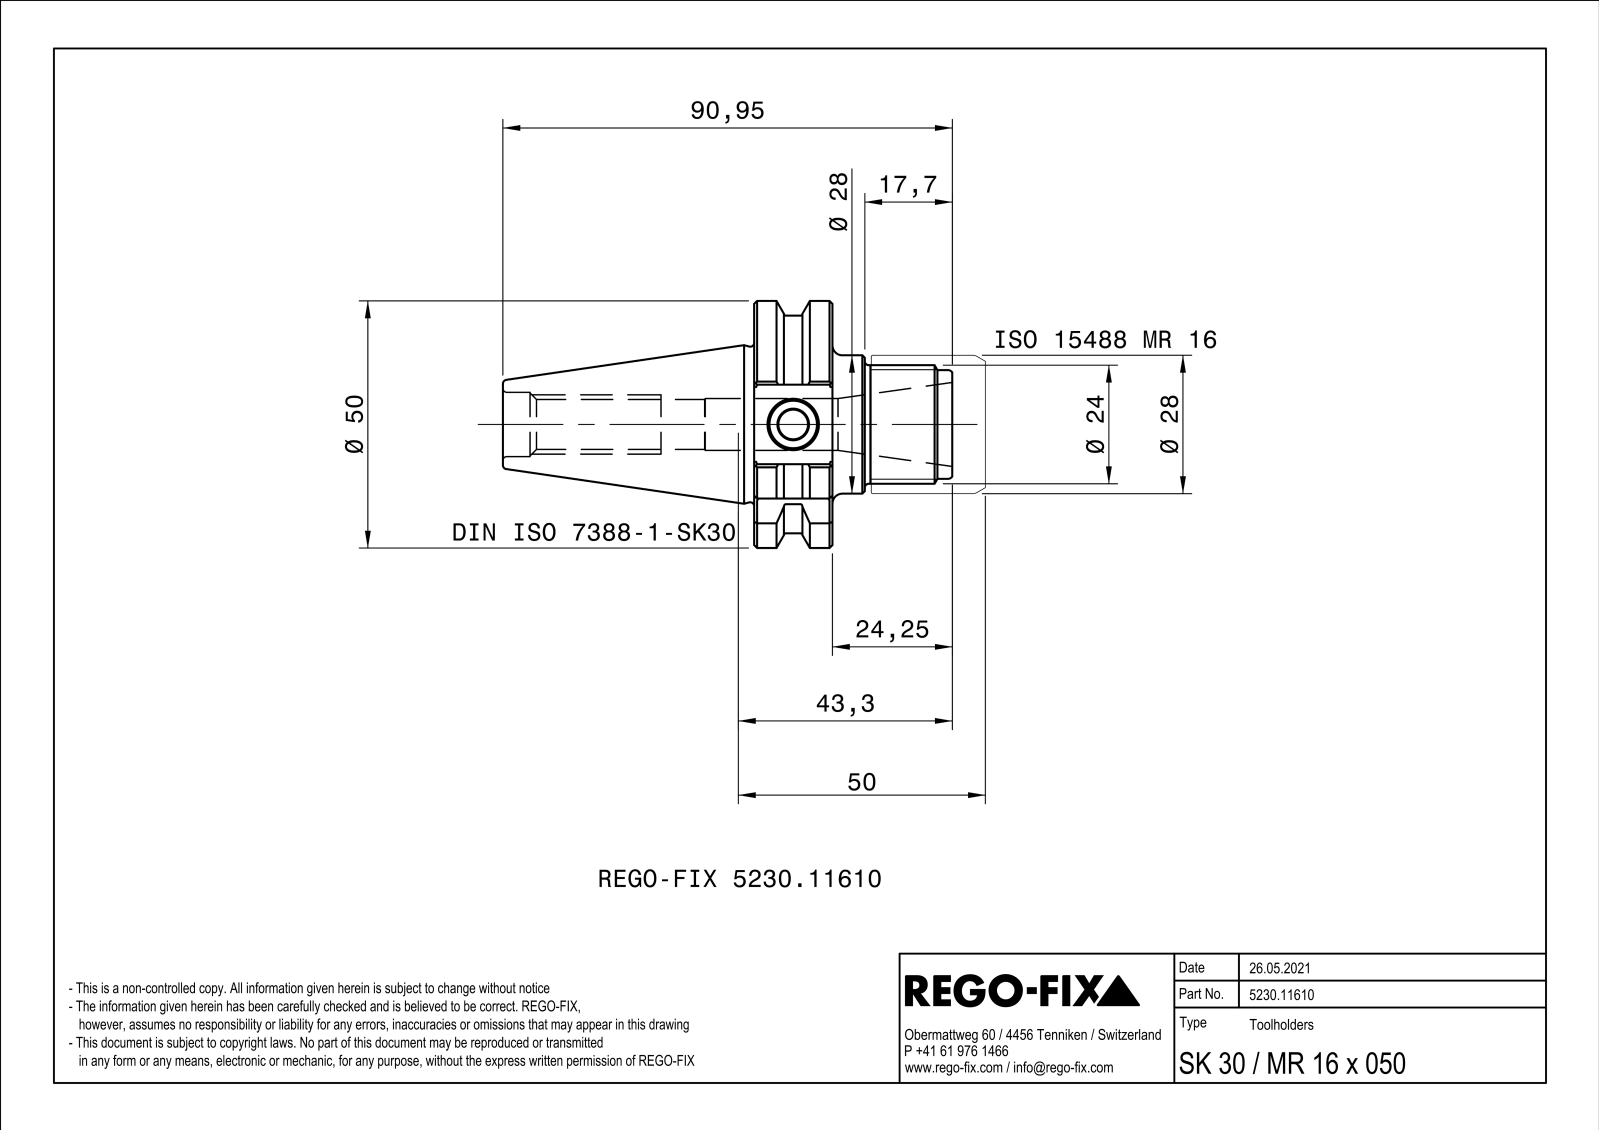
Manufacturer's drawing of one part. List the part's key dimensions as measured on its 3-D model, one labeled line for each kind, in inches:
Part name (STEP PRODUCT): NOCUT
STEP written by: SIEMENS PLM Software Solid Edge ST10 (AUTOMOTIVE_DESIGN)
Units: inches
Bodies: 1 solid, 115 faces (44 planar, 34 cylindrical, 37 other)
Overall size (bounding box): 3.581 × 1.969 × 1.846
Volume: 3.266 in³ · Surface area: 22.96 in²
Round holes (diameter × count): ⌀0.236 ×1, ⌀0.394 ×1, ⌀0.398 ×1, ⌀0.413 ×1, ⌀0.512 ×1
Round bosses / shafts (diameter × count): ⌀1.102 ×1, ⌀0.945 ×1, ⌀0.866 ×1
Partial cylindrical surfaces — rounded edges, fillets, slot ends (radius × count): R0.02 ×13, R0.551 ×1, R0.867 ×1, R0.984 ×1
Main face-to-face distances: 0.624, 1.378, 0.634, 0.955, 1.579, 0.697, 0.258, 0.882, 0.274, 0.907
